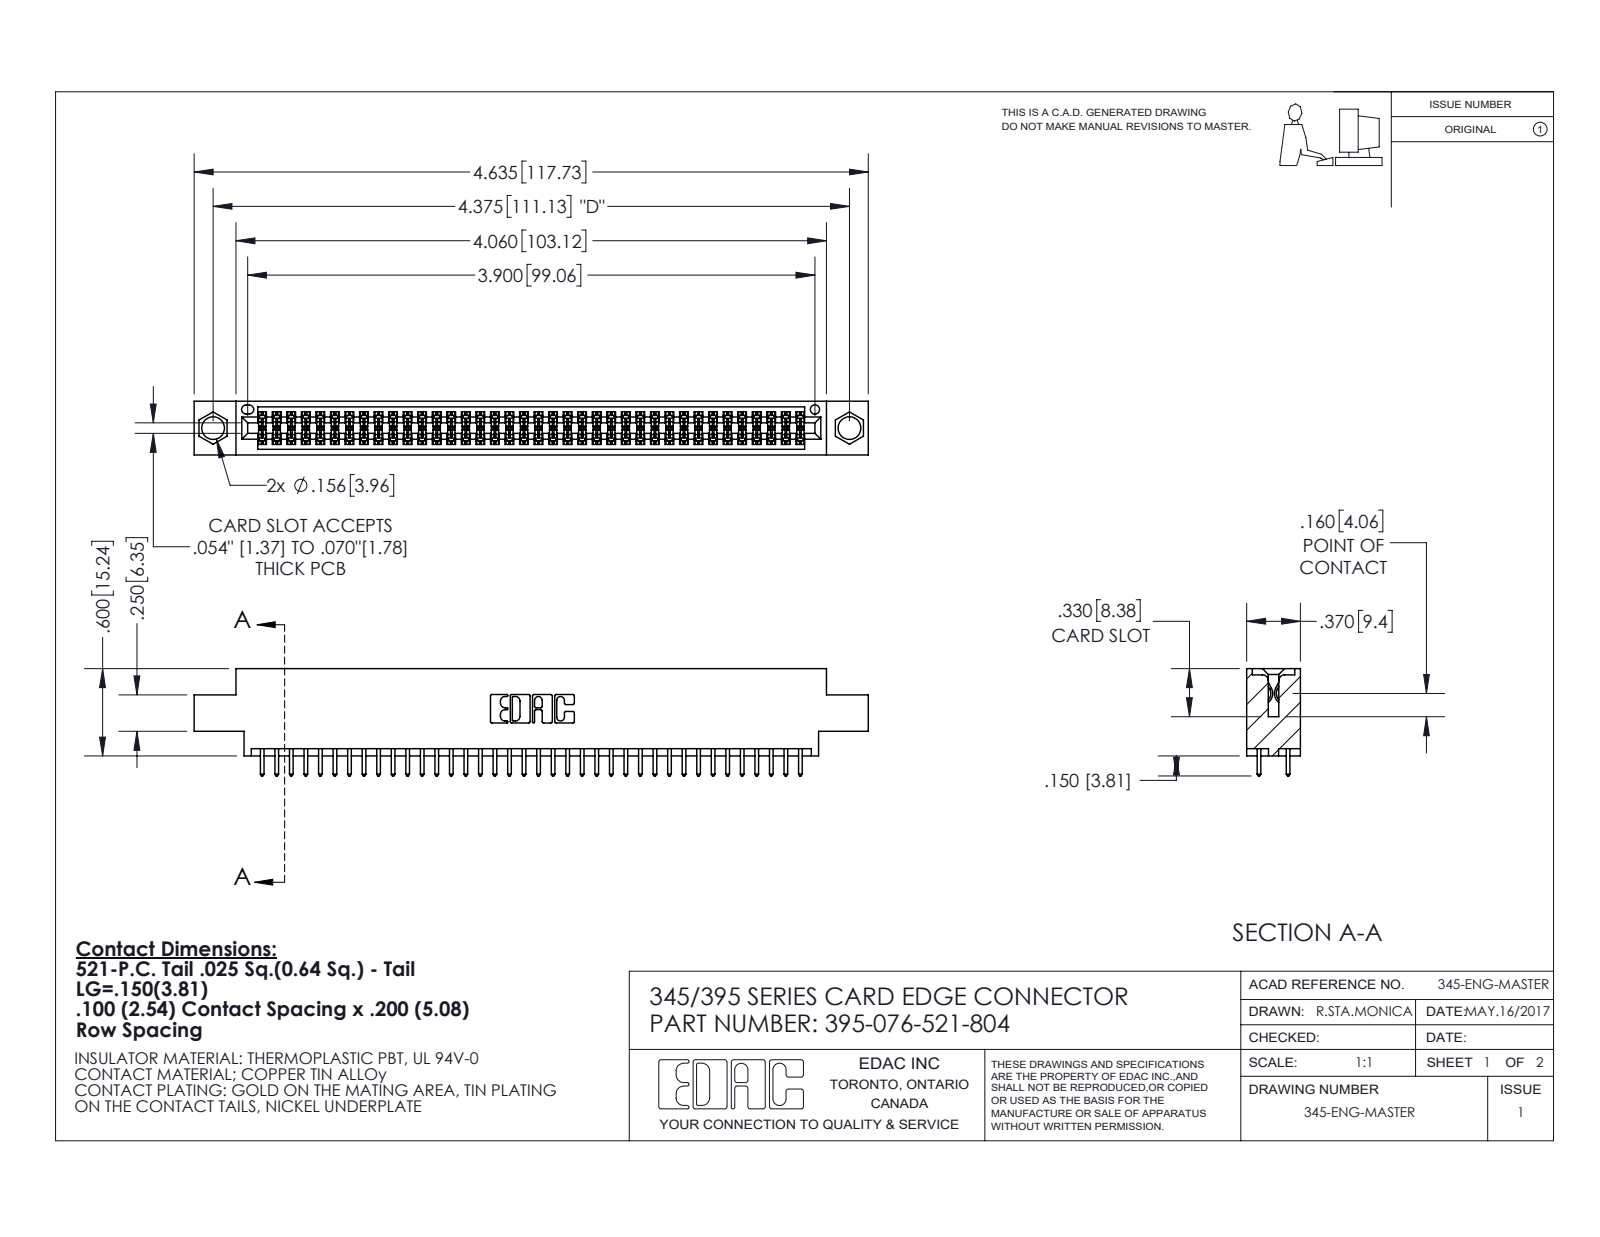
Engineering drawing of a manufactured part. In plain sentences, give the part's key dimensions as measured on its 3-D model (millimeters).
The part is named "345 Part_0.170 Offset - 0.156 Dia-TI; 345-292-001_345-293-121; 395-076-521-804". Its 3-D file was written by "SolidWorks 2020 (CONFIG_CONTROL_DESIGN)". It is 77 solids with 3944 faces: 2606 planar, 1338 cylindrical and 0 other. Overall it measures 117.7 by 18.7 by 9.4 millimeters. Its volume is 11 100 cubic millimeters and its surface area 16 190 square millimeters. Round holes: 2 of diameter 4, 1 of diameter 1.6. Partial cylindrical surfaces (rounded edges, fillets, slot ends): 152 of radius 0.2, 76 of radius 0.3, 22 of radius 0.3, 6 of radius 0.2, 6 of radius 0.8, 3 of radius 0.7, 2 of radius 0.4, 2 of radius 0.5. The main face-to-face distances are 1.8, 7.6, 5.1, 9.4, 2.5, 6.9, 0.6, 5.7, 4.4, 3.8. The hole center spacings are 6.9, 105.1, 111.1.
